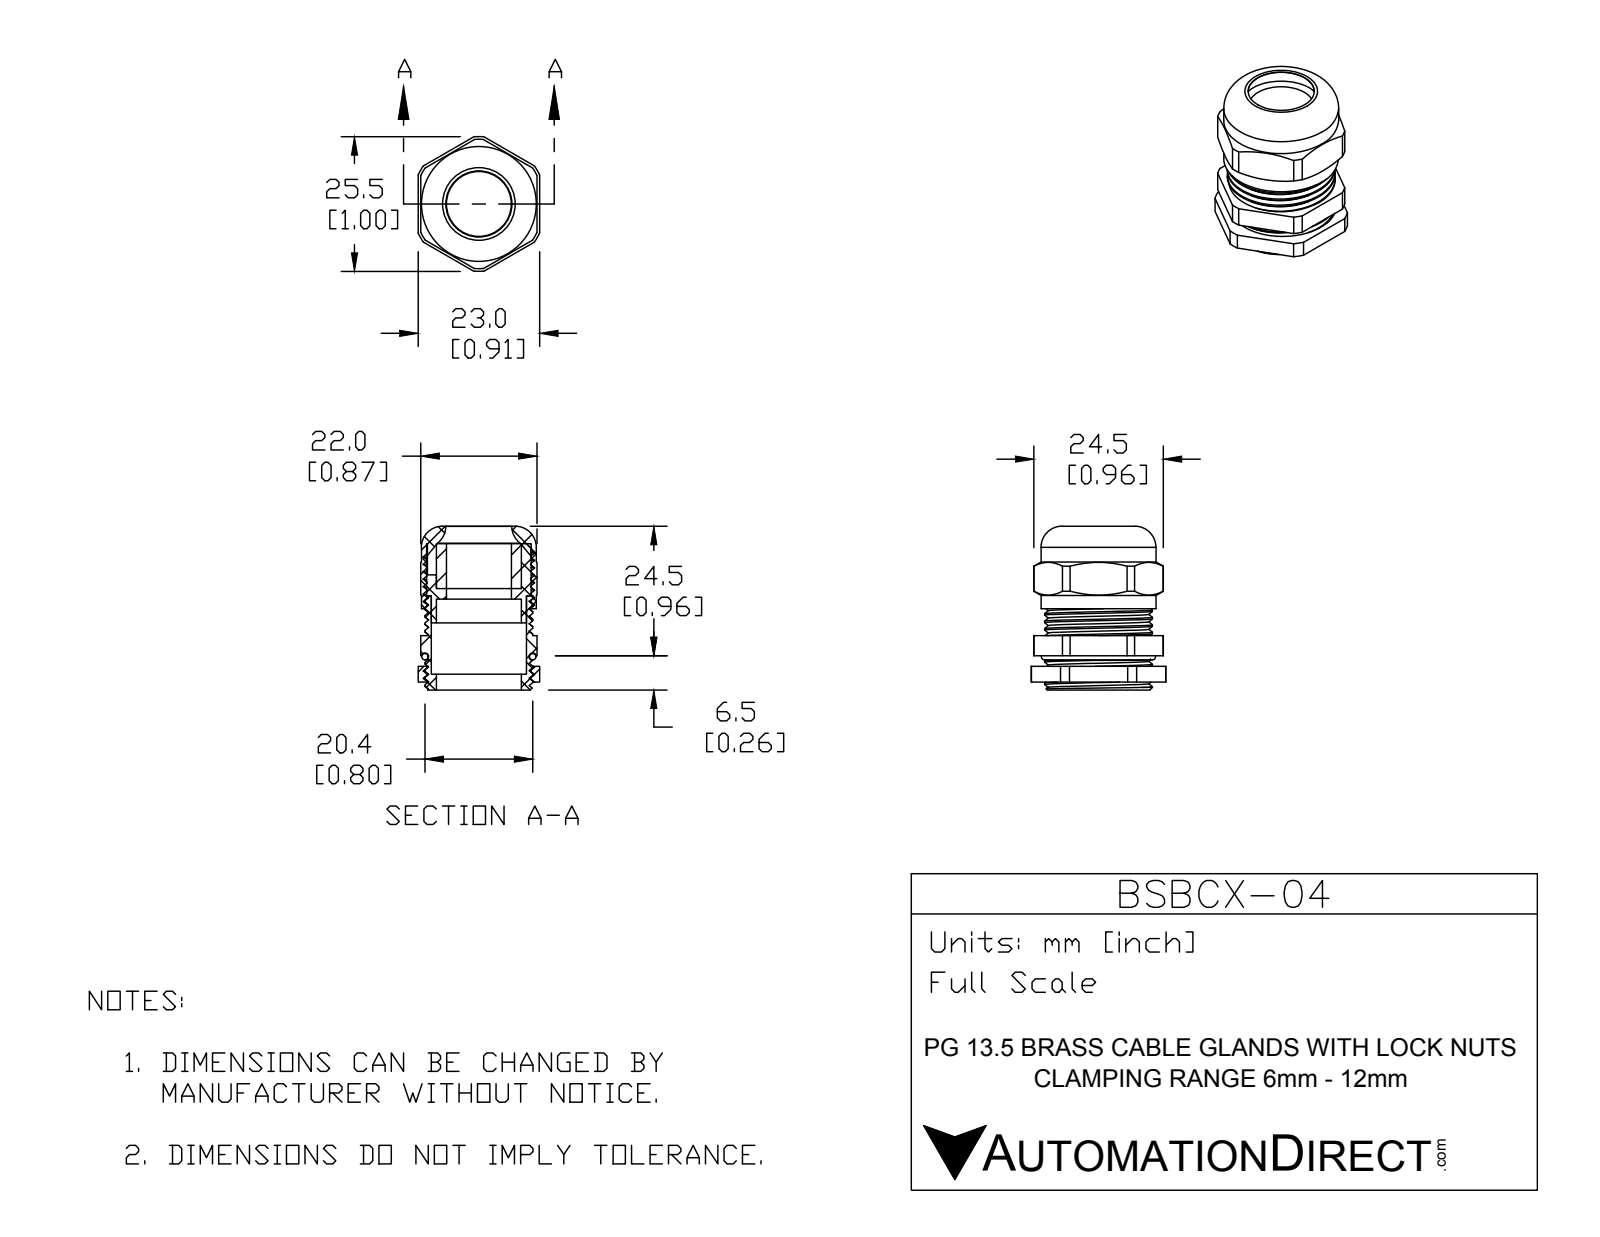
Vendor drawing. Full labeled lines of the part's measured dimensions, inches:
Part name (STEP PRODUCT): BSBCX-04
STEP written by: SolidWorks 2015 (CONFIG_CONTROL_DESIGN)
Units: inches
Bodies: 6 solids, 254 faces (135 planar, 86 cylindrical, 33 other)
Overall size (bounding box): 1.22 × 1.004 × 0.906
Volume: 0.339 in³ · Surface area: 15.62 in²
Round holes (diameter × count): ⌀0.484 ×1, ⌀0.492 ×1, ⌀0.634 ×1, ⌀0.709 ×1, ⌀0.777 ×1
Round bosses / shafts (diameter × count): ⌀0.856 ×1, ⌀0.803 ×1, ⌀0.78 ×1
Partial cylindrical surfaces — rounded edges, fillets, slot ends (radius × count): R0.482 ×1, R0.502 ×1
Main face-to-face distances: 0.02, 0.866, 0.886, 0.059, 0.118, 0.5, 0.335, 0.35, 0.177, 0.697
